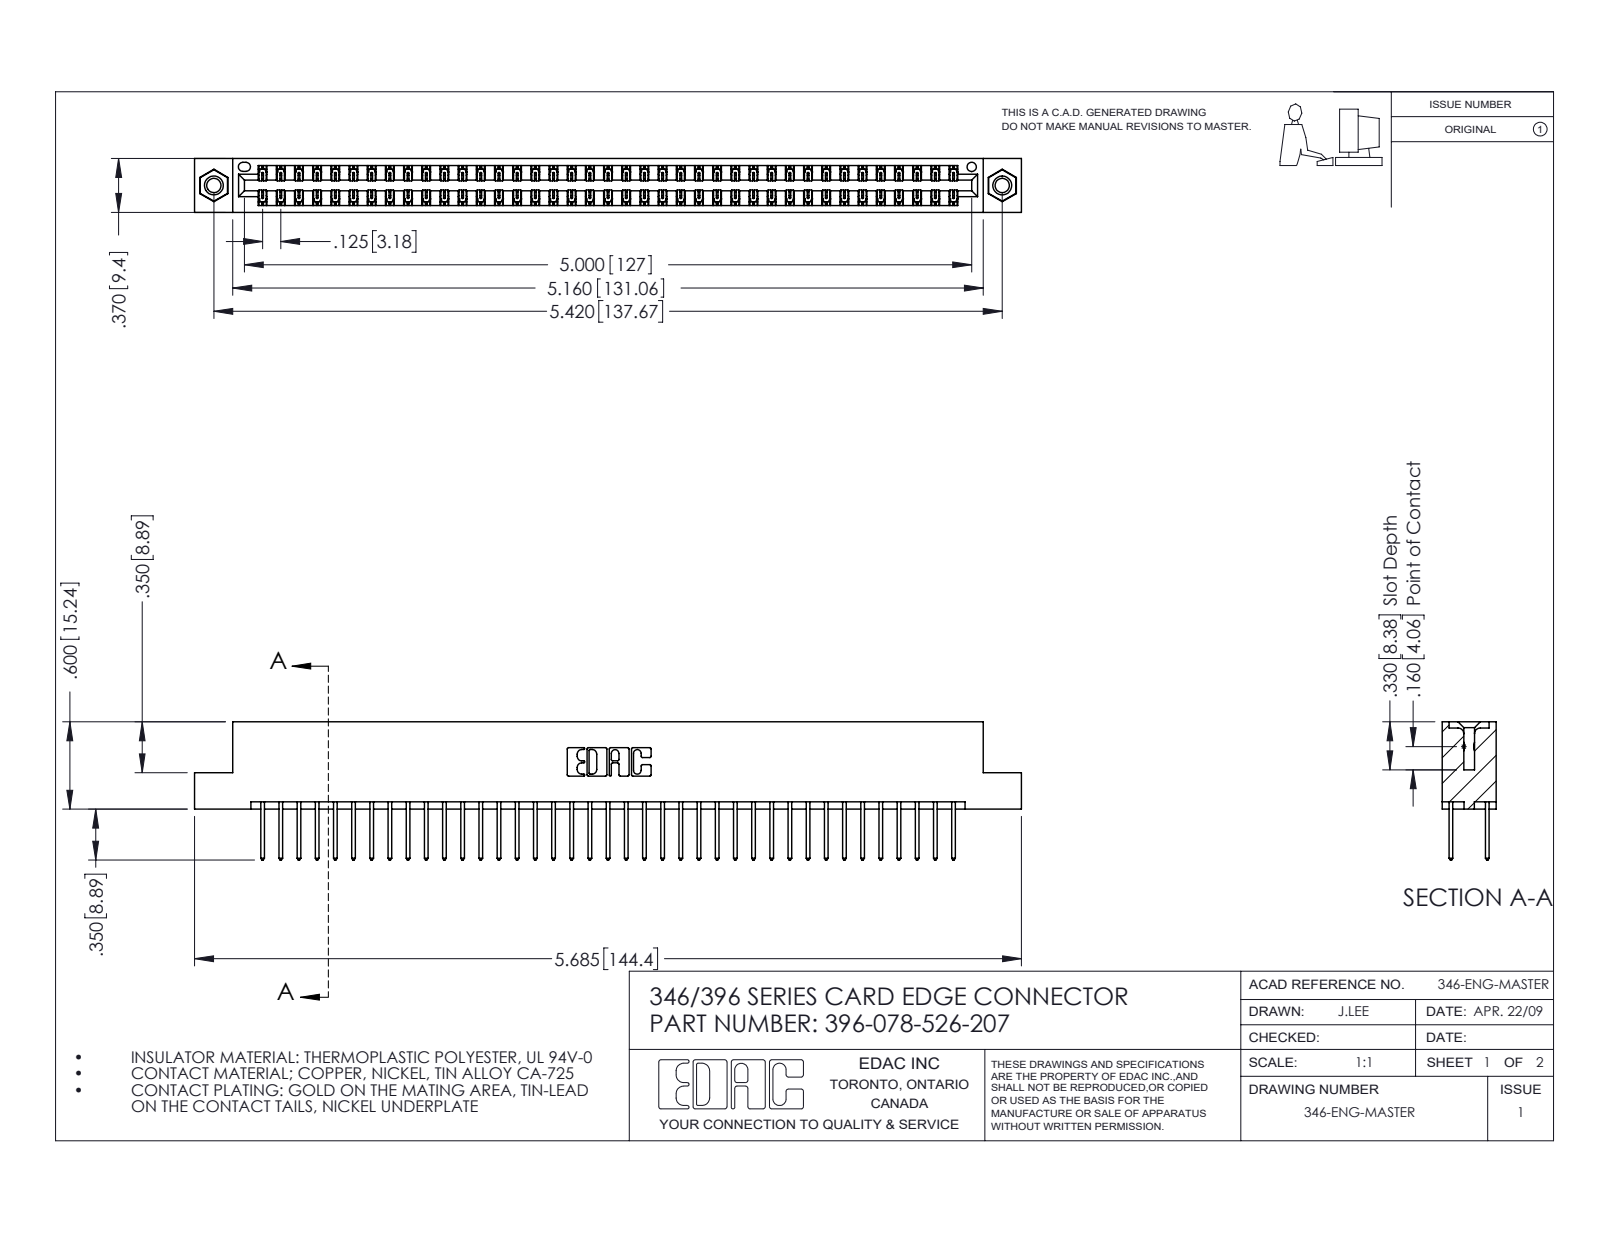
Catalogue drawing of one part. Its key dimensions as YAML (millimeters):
part_name: "396-078-526-207; 346 Part_Flush Mounting Lugs - 0.156 Dia-TI; 345-250-001_345-250-005-103; 345-292-001_345-293-126"
step_written_by: "SolidWorks 2016 (CONFIG_CONTROL_DESIGN)"
units: millimeters
bodies: {solids: 81, faces: 4238, planar: 2838, cylindrical: 1384, other: 16}
overall_size: [144.4, 24.1, 9.4]
volume: 14200
surface_area: 20040
round_holes:
  - {diameter: 2.5, count: 2}
  - {diameter: 3.2, count: 2}
  - {diameter: 4, count: 2}
  - {diameter: 1.6, count: 1}
round_bosses_or_shafts:
  - {diameter: 3.9, count: 2}
partial_cylinders:
  - {radius: 0.2, count: 117}
  - {radius: 0.3, count: 78}
  - {radius: 0.3, count: 22}
  - {radius: 0.2, count: 6}
  - {radius: 0.8, count: 6}
  - {radius: 0.7, count: 3}
  - {radius: 0.4, count: 2}
  - {radius: 0.6, count: 2}
face_to_face_distances: [1.2, 8.2, 6.4, 9.4, 1.8, 7.6, 0.6, 7, 3.8, 5.6]
hole_center_spacings: [6.2, 132.4, 137.7]
